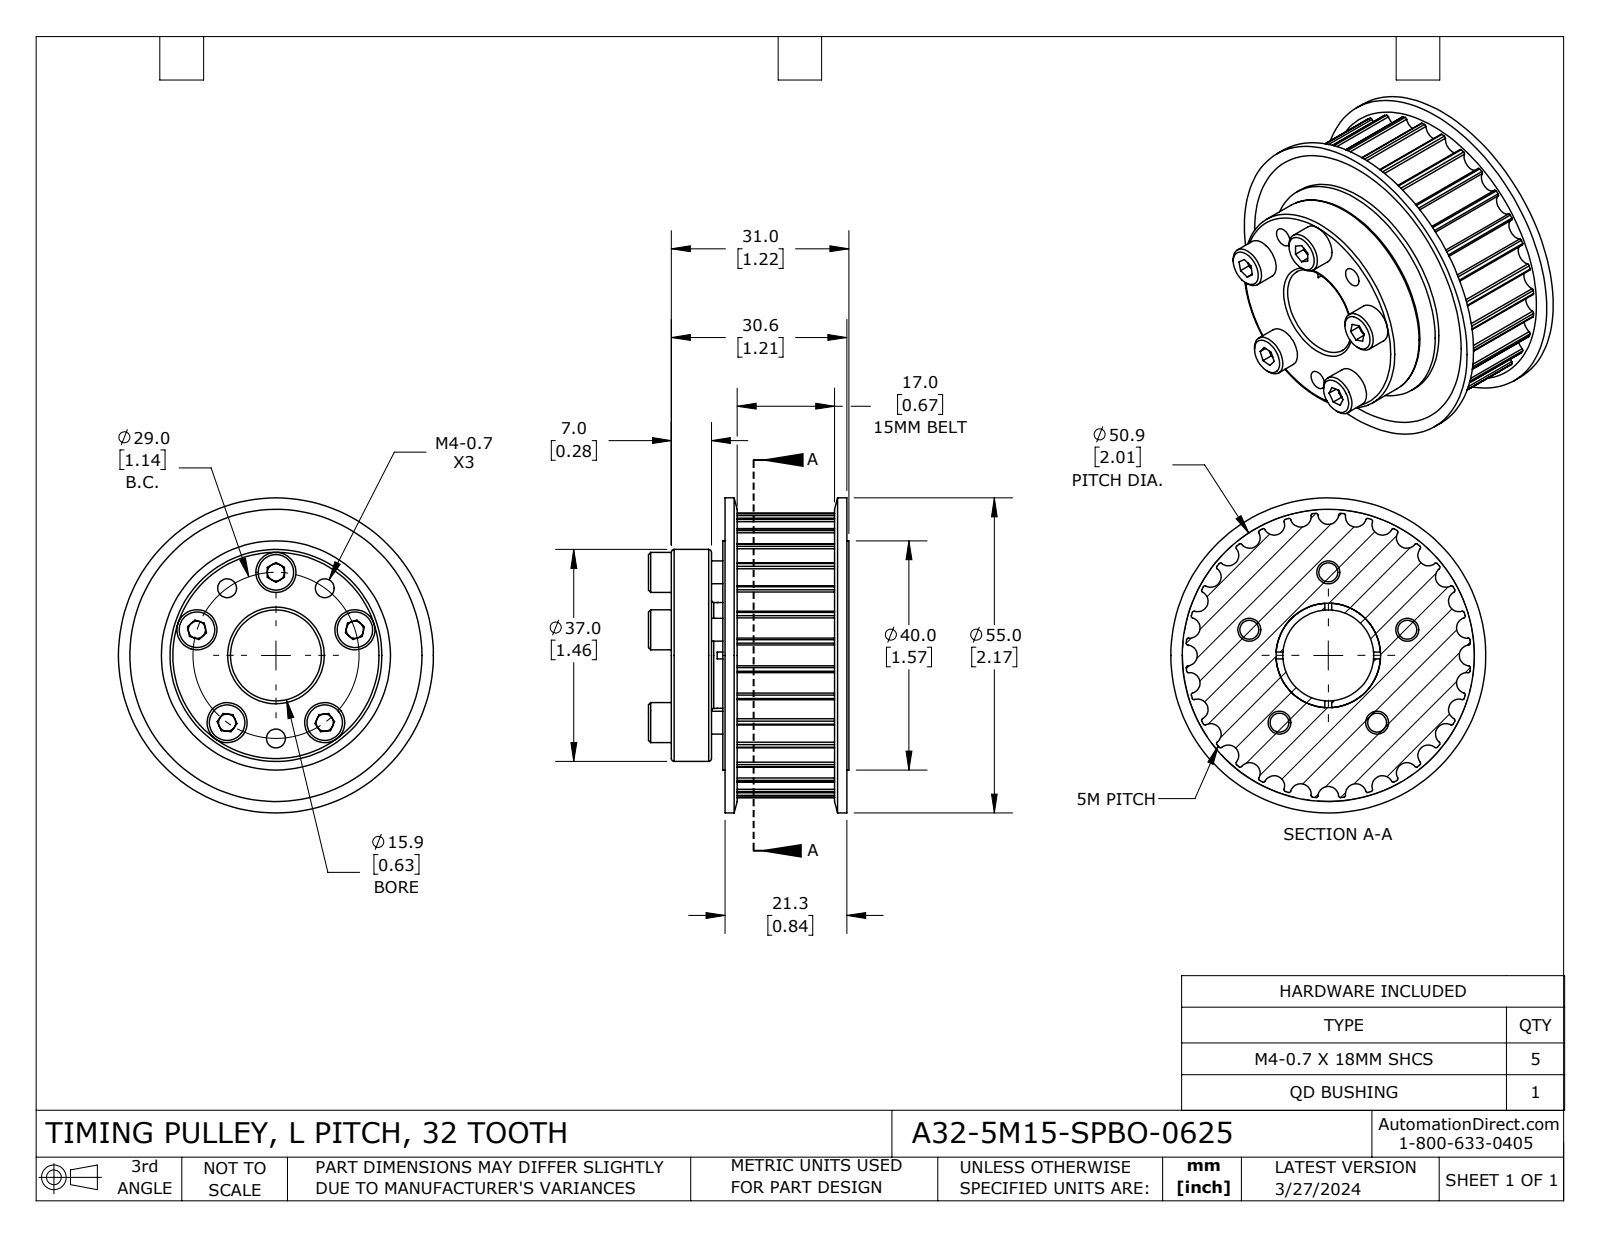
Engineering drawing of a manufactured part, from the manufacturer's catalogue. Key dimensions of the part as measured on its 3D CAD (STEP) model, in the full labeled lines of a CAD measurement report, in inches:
Part name (STEP PRODUCT): A32-5M15-SPBO-0625
STEP written by: SolidWorks 2021 (CONFIG_CONTROL_DESIGN)
Units: inches
Bodies: 9 solids, 394 faces (101 planar, 227 cylindrical, 66 other)
Overall size (bounding box): 2.165 × 2.165 × 1.378
Volume: 2.562 in³ · Surface area: 33.92 in²
Round holes (diameter × count): ⌀0.13 ×8, ⌀0.177 ×5, ⌀0.625 ×1, ⌀0.727 ×1, ⌀1.575 ×1
Round bosses / shafts (diameter × count): ⌀0.276 ×5, ⌀0.157 ×5, ⌀2.165 ×1, ⌀1.457 ×1
Partial cylindrical surfaces — rounded edges, fillets, slot ends (radius × count): R0.012 ×64, R0.072 ×32, R0.98 ×1
Main face-to-face distances: 0.098, 0.768, 0.035, 0.831, 0.063, 0.732, 0.669, 0.866, 0.354, 0.453
Hole centre spacings: 0.571, 1.086, 0.353, 0.924, 0.671, 1.142, 0.671
